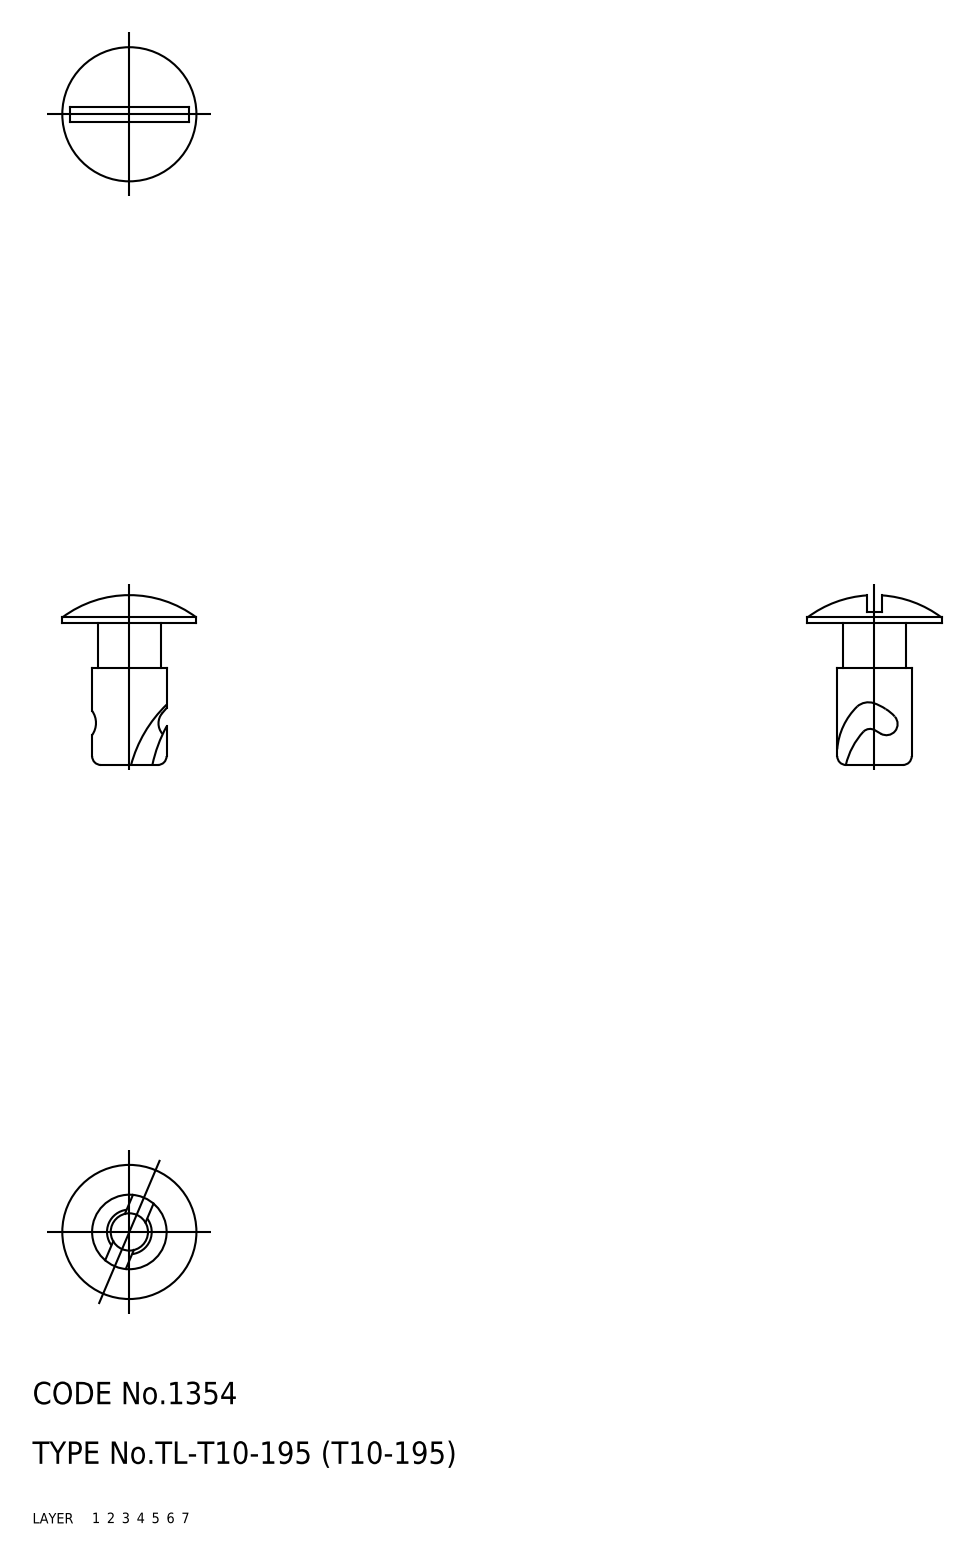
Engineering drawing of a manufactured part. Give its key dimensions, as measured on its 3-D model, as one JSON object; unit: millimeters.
{"part_name": "fastener", "step_written_by": "CADfix (AUTOMOTIVE_DESIGN)", "units": "millimeters", "bodies": {"solids": 1, "faces": 36, "planar": 0, "cylindrical": 0, "other": 36}, "overall_size": [22.77, 18, 18], "volume_mm3": 1565, "surface_area_mm2": 1357}
